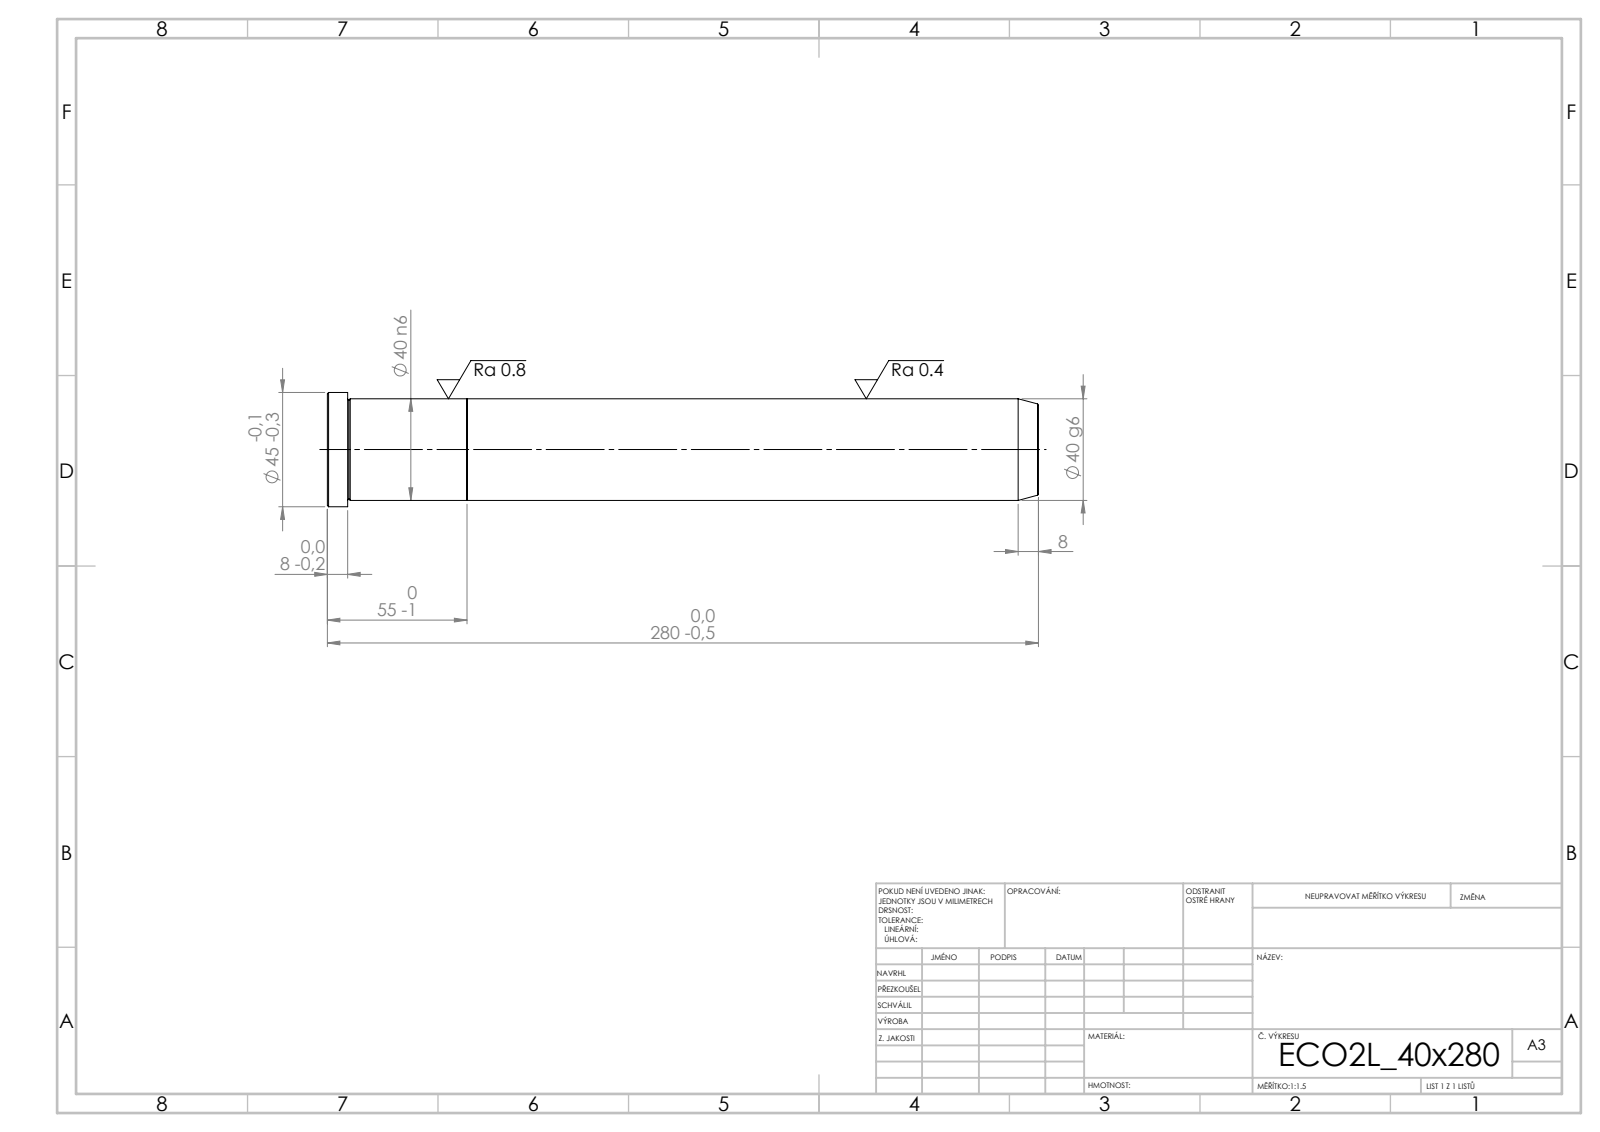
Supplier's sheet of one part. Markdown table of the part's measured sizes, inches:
| quantity | value |
| --- | --- |
| STEP written by | SolidWorks 2019 (CONFIG_CONTROL_DESIGN) |
| units | inches |
| bodies | 2 solids, 21 faces (5 planar, 6 cylindrical, 10 other) |
| overall size | 11.024 × 1.772 × 1.772 |
| volume | 21.57 in³ |
| surface area | 63.15 in² |
| round bosses / shafts (diameter × count) | 1.772 × 1, 1.575 × 1 |
| main face-to-face distances | 2.165, 8.858, 11.024, 10.709, 1.85, 0.315 |
